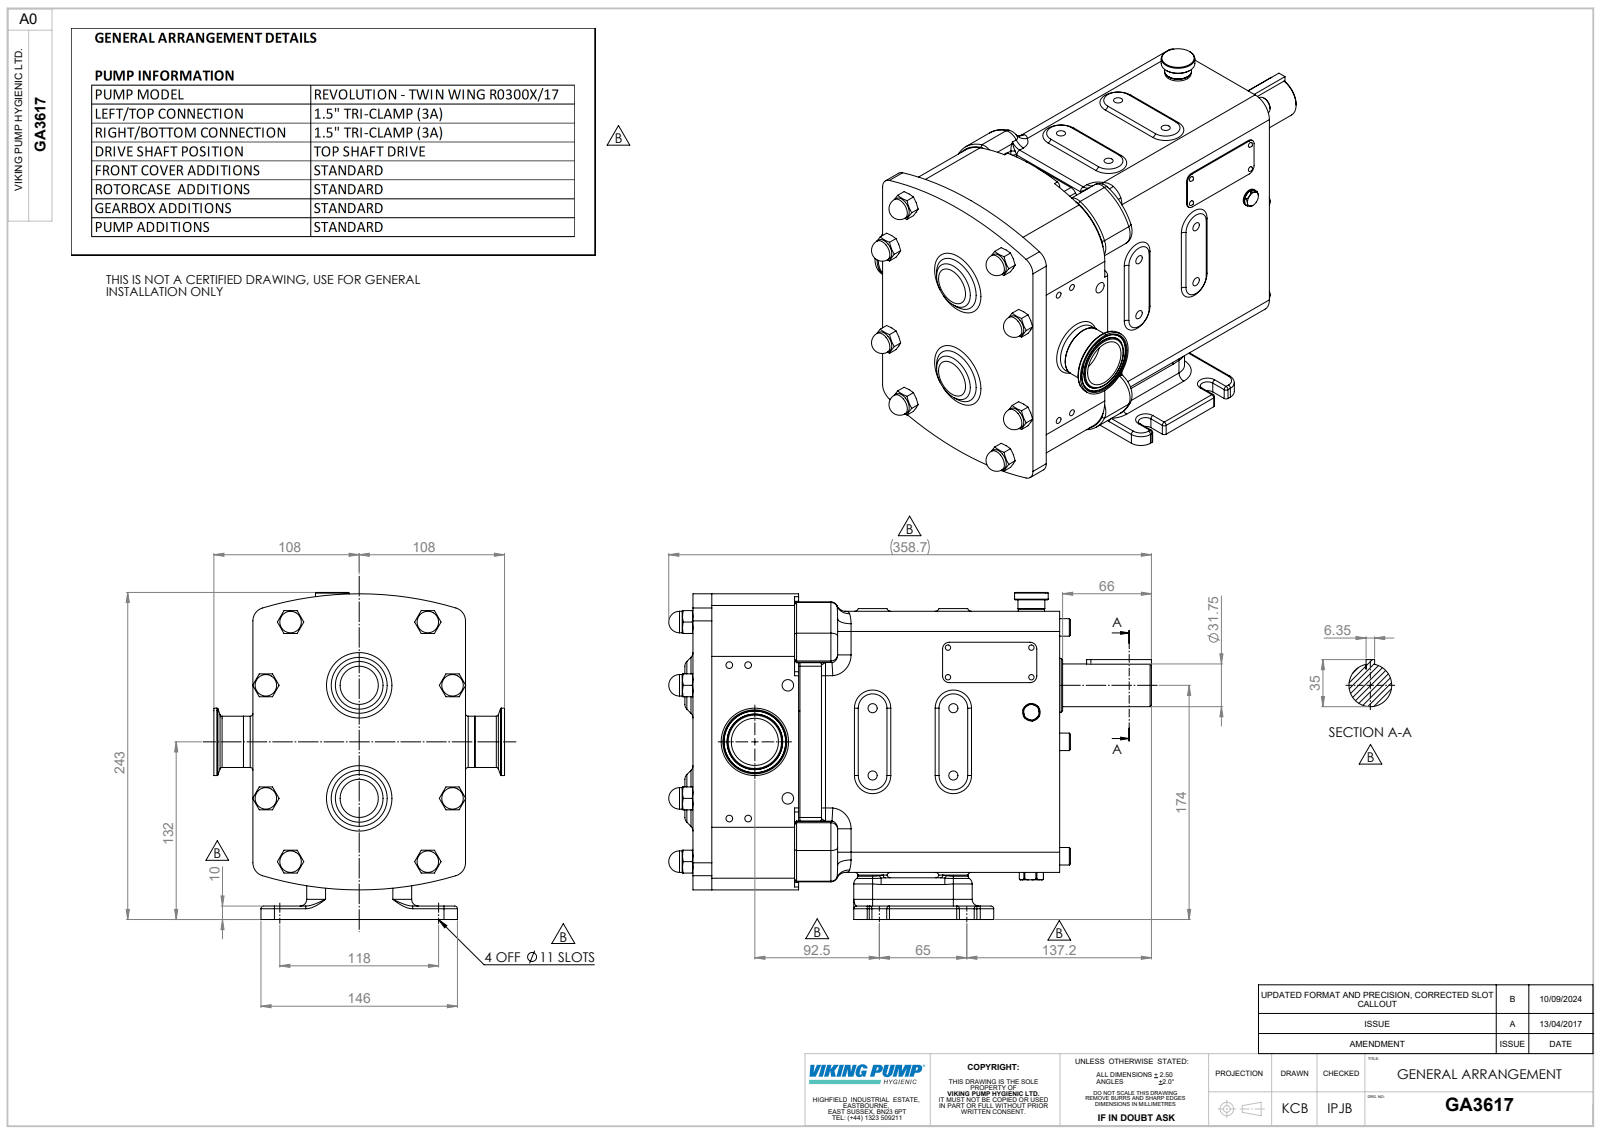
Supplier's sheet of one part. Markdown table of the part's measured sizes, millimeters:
| quantity | value |
| --- | --- |
| part name | Copy of RA94-5121-22M^GA3617; GA3617; Copy of R0300 CPP H TSD^GA3617 |
| STEP written by | SolidWorks 2023 (AUTOMOTIVE_DESIGN) |
| units | millimeters |
| bodies | 3 solids, 981 faces (304 planar, 306 cylindrical, 371 other) |
| overall size | 358.7 × 243 × 216 |
| volume | 6 975 000 mm³ |
| surface area | 368 628 mm² |
| round holes (diameter × count) | 6.8 × 8, 5 × 4, 8.57 × 2, 23 × 1, 35.05 × 1 |
| round bosses / shafts (diameter × count) | 16 × 8, 13 × 7, 50.1 × 1, 40 × 1, 38.1 × 1, 38 × 1, 31.75 × 1, 25 × 1 |
| partial cylindrical surfaces (radius × count) | 10 × 30, 3 × 28, 2 × 24, 5 × 19, 5.9 × 8, 15 × 8, 5.5 × 4, 8 × 4 |
| main face-to-face distances | 194, 24, 110, 272.5, 134, 78.5, 79.5, 193, 1, 4 |
| hole center spacings | 50, 60, 78.1, 14, 33.11, 46.03, 48.63, 57.22 |
